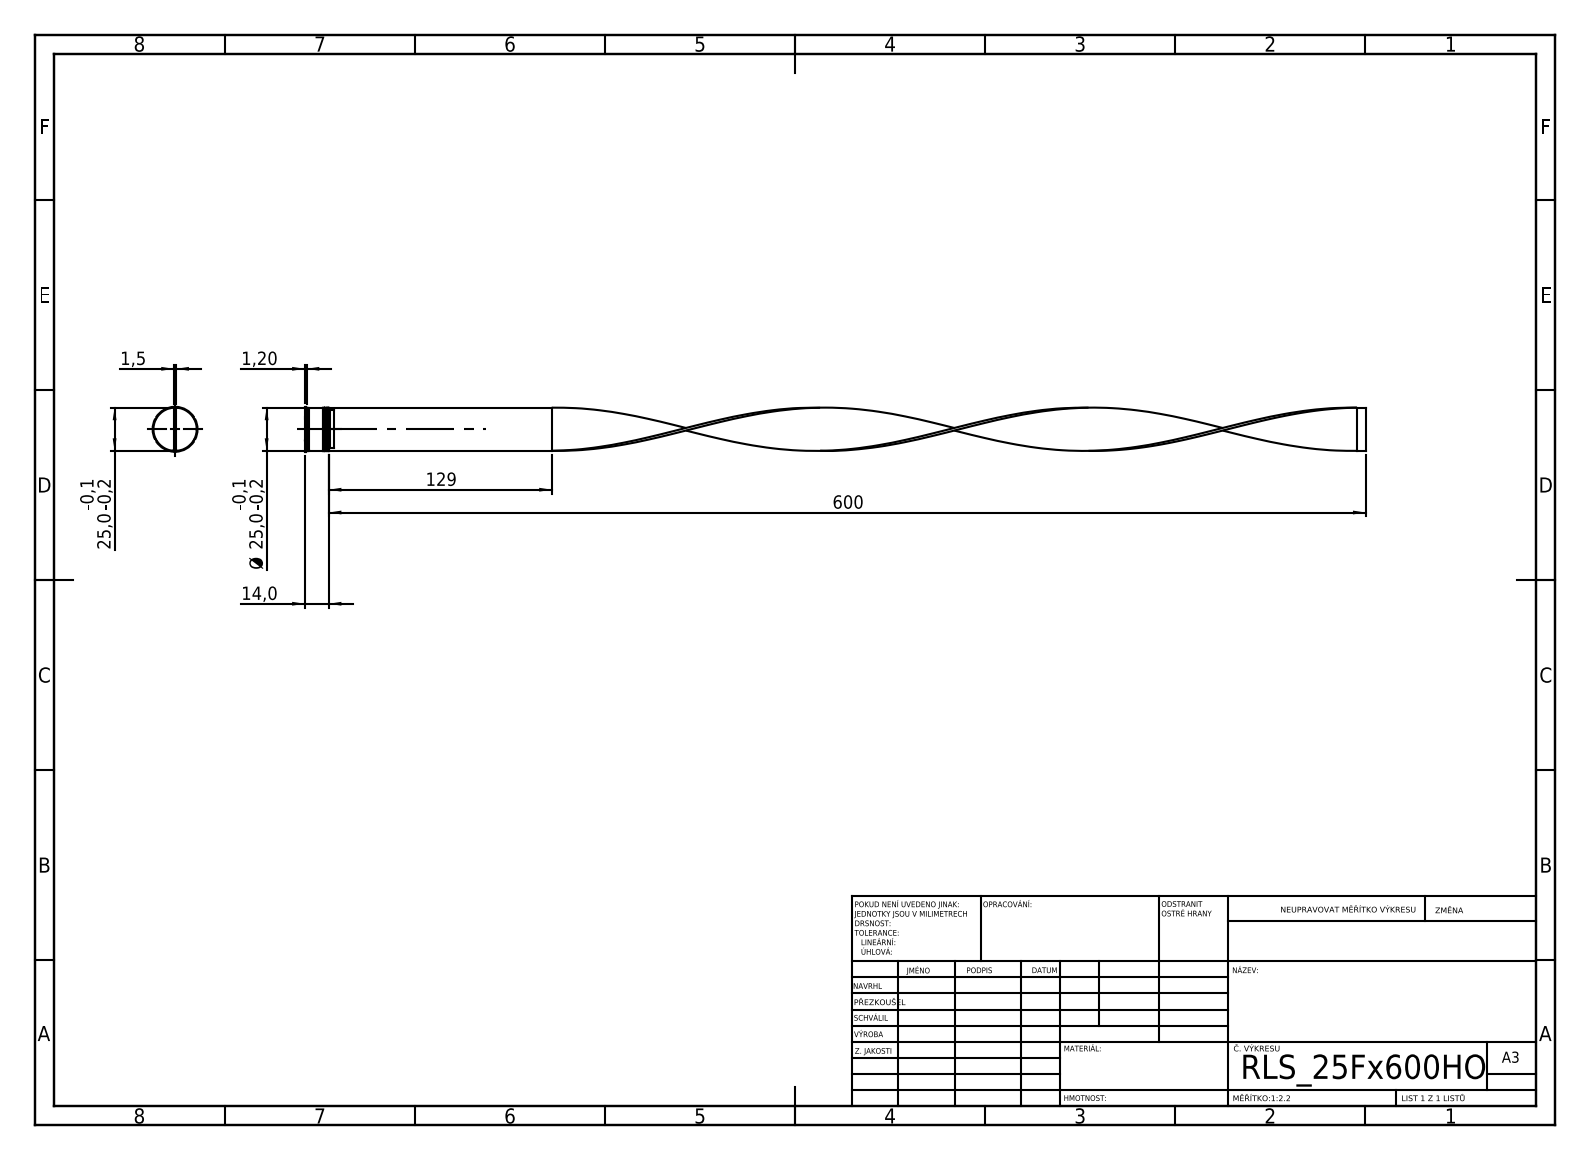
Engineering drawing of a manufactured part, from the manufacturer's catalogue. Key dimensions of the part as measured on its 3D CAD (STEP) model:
STEP written by: SolidWorks 2019 (CONFIG_CONTROL_DESIGN)
Units: millimetres
Bodies: 3 solids, 108 faces (48 planar, 33 cylindrical, 27 other)
Overall size (bounding box): 614 × 26 × 25.98
Volume: 30 629 mm³ · Surface area: 36 496 mm²
Round bosses / shafts (diameter × count): ⌀26 ×1, ⌀25 ×1, ⌀24.4 ×1, ⌀21.8 ×1
Partial cylindrical surfaces — rounded edges, fillets, slot ends (radius × count): R11 ×1
Main face-to-face distances: 1.5, 0.7, 2.2, 0.8, 11.7, 11, 10.2, 9.5, 4.3, 5
